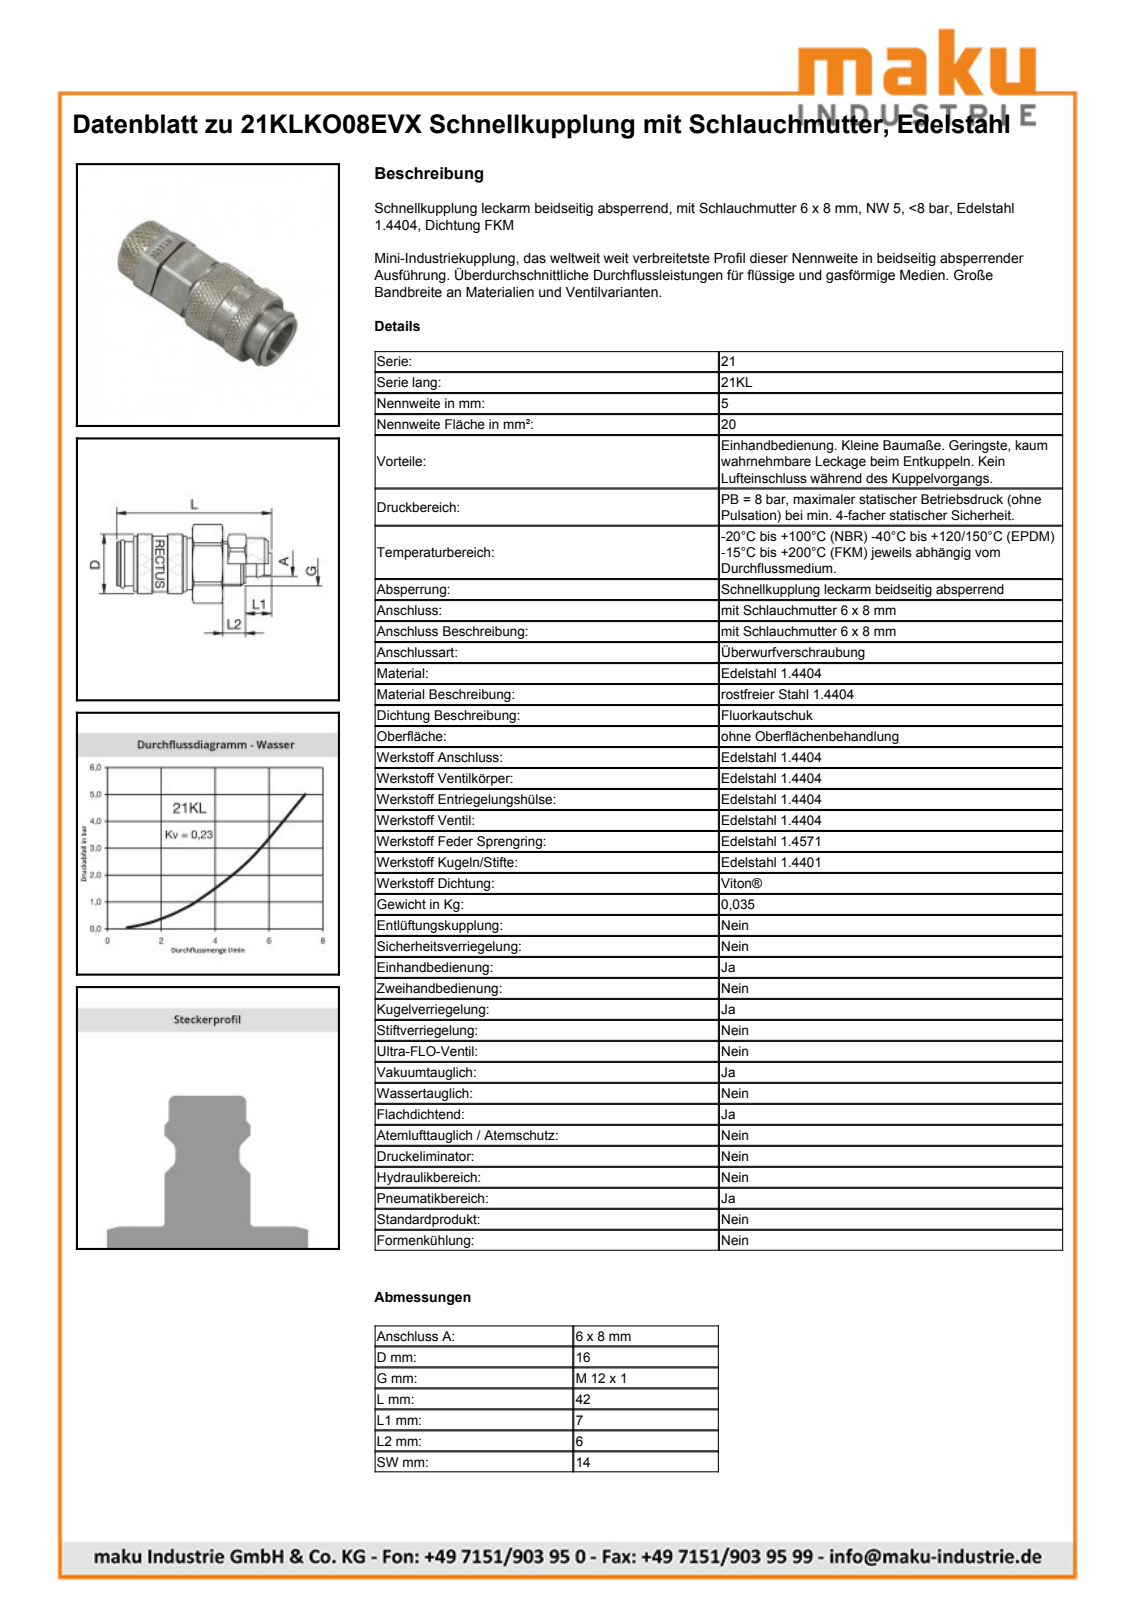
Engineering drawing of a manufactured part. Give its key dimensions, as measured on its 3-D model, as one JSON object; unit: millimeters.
{"part_name": "D109966", "step_written_by": "Autodesk Inventor 2013 (AUTOMOTIVE_DESIGN)", "units": "millimeters", "bodies": {"solids": 2, "faces": 473, "planar": 148, "cylindrical": 76, "other": 249}, "overall_size": [42.15, 16, 16], "volume_mm3": 6010, "surface_area_mm2": 4562, "round_holes": [[10.7, 1], [11, 1], [12.1, 1], [12.15, 1], [12.5, 1], [12.6, 1], [12.75, 1], [14.6, 1]], "round_bosses_or_shafts": [[16, 1], [15, 1], [14, 1], [12, 1], [11.4, 1], [11.15, 1], [10.4, 1], [10.25, 1]], "partial_cylinders_radius": [[7.4, 1], [7.75, 1], [7.9, 1]], "face_to_face_distances": [14, 1.1, 12.1, 4.5, 35.05, 30.55, 28.95, 24.45, 6.1, 41.05]}
